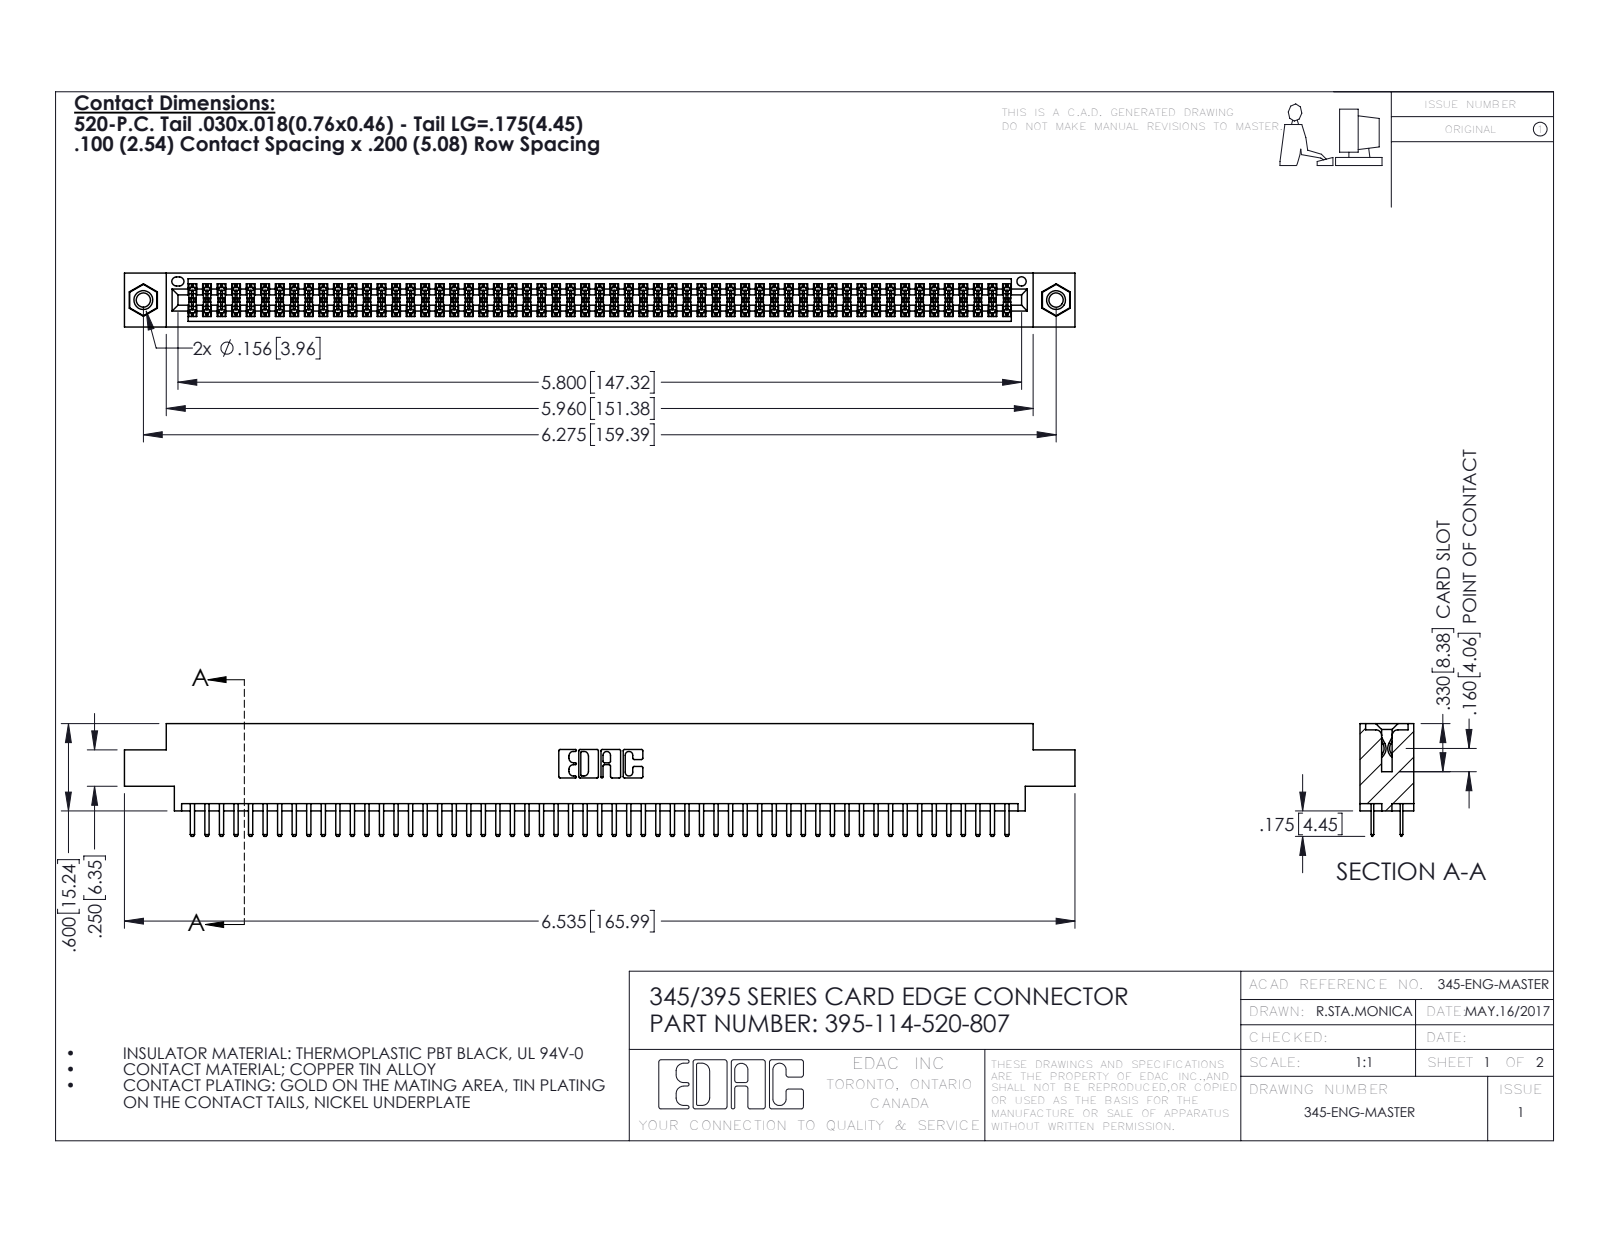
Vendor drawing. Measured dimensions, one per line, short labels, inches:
name: 345-292-001_345-293-120; 345-250-001_345-250-005-103; 395-114-520-807; 345 Part_0.170 Offset - 0.156 Dia-TI
written by: SolidWorks 2016 (CONFIG_CONTROL_DESIGN)
unit: in
bodies: 117 solids, 6346 faces (4106 planar, 2224 cylindrical, 16 other)
size: 6.535 × 0.775 × 0.37
volume: 0.982 in³; area: 37.41 in²
holes: 2× ⌀0.098, 2× ⌀0.125, 2× ⌀0.156, 1× ⌀0.064
bosses: 2× ⌀0.155
rounds: 171× R0.006, 118× R0.01, 22× R0.01, 6× R0.007, 6× R0.031, 3× R0.026, 2× R0.014, 2× R0.019
face distances: 0.072, 0.298, 0.2, 0.37, 0.098, 0.272, 0.025, 0.225, 0.022, 0.072
hole spacings: 0.27, 6.039, 6.275
